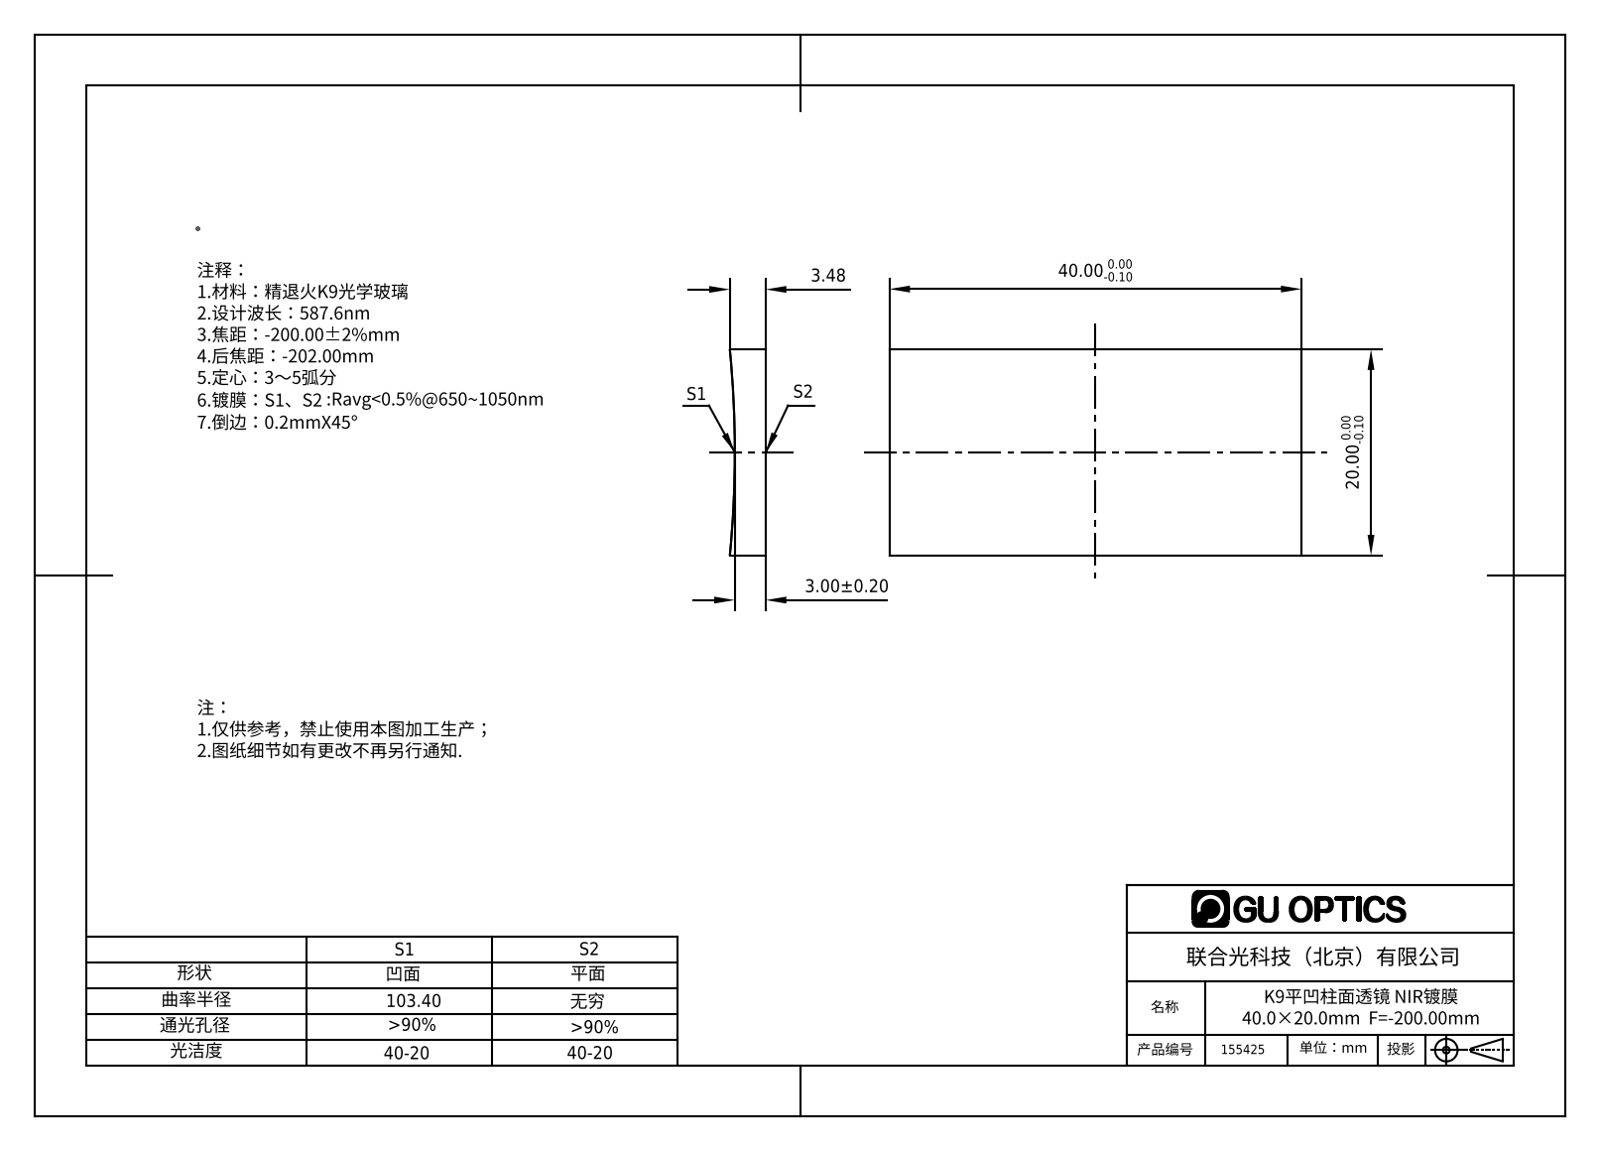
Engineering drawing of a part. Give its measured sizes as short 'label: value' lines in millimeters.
name: 155359
written by: SolidWorks 2016 (AUTOMOTIVE_DESIGN)
unit: mm
bodies: 1 solid, 6 faces (5 planar, 1 cylindrical, 0 other)
size: 40 × 20 × 3.48
volume: 2 529 mm³; area: 2 006 mm²
rounds: 1× R103.4
face distances: 20, 40
